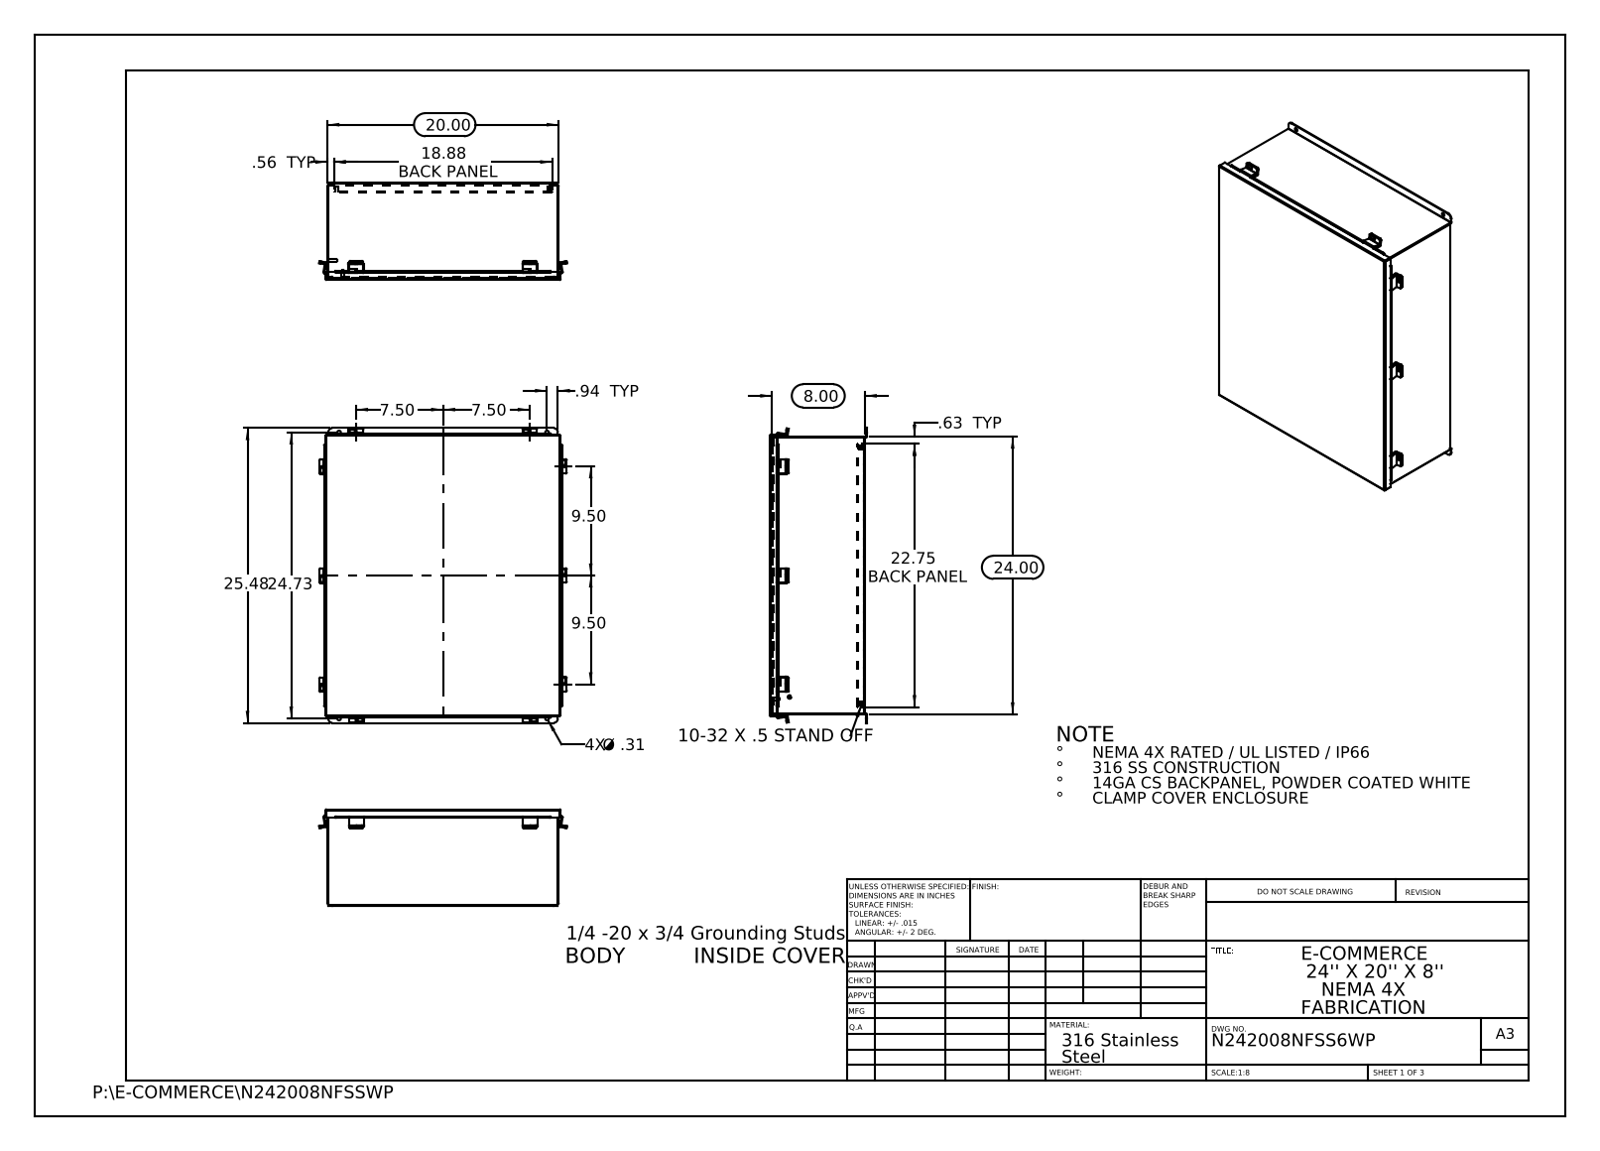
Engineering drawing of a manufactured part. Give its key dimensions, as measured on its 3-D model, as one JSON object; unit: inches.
{"part_name": "N242008NFSSWP JIC Clamp Bracket; N242008NFSSWP JIC Backpanel; N242008NFSSWP JIC_Standoff; N242008NFSSWP JIC_Cover_Template (+6 more)", "step_written_by": "SolidWorks 2013 (CONFIG_CONTROL_DESIGN)", "units": "inches", "bodies": {"solids": 31, "faces": 732, "planar": 484, "cylindrical": 228, "other": 20}, "overall_size": [25.476, 21.407, 8.39], "volume_in3": 168.7, "surface_area_in2": 4548, "round_holes": [[0.25, 14], [0.187, 4], [0.312, 4]], "round_bosses_or_shafts": [[0.313, 4], [0.315, 2], [0.236, 2]], "partial_cylinders_radius": [[0.125, 38], [0.133, 20], [0.009, 16], [0.013, 12], [0.088, 12], [0.083, 8], [0.1, 8], [0.084, 4]], "face_to_face_distances": [0.075, 8.128, 8.053, 8.203, 7.628, 0.575, 0.5, 7.553, 0.649, 0.574], "hole_center_spacings": [1.315, 9.425, 18.222, 23.427, 29.65, 15, 17.976, 18.375]}
